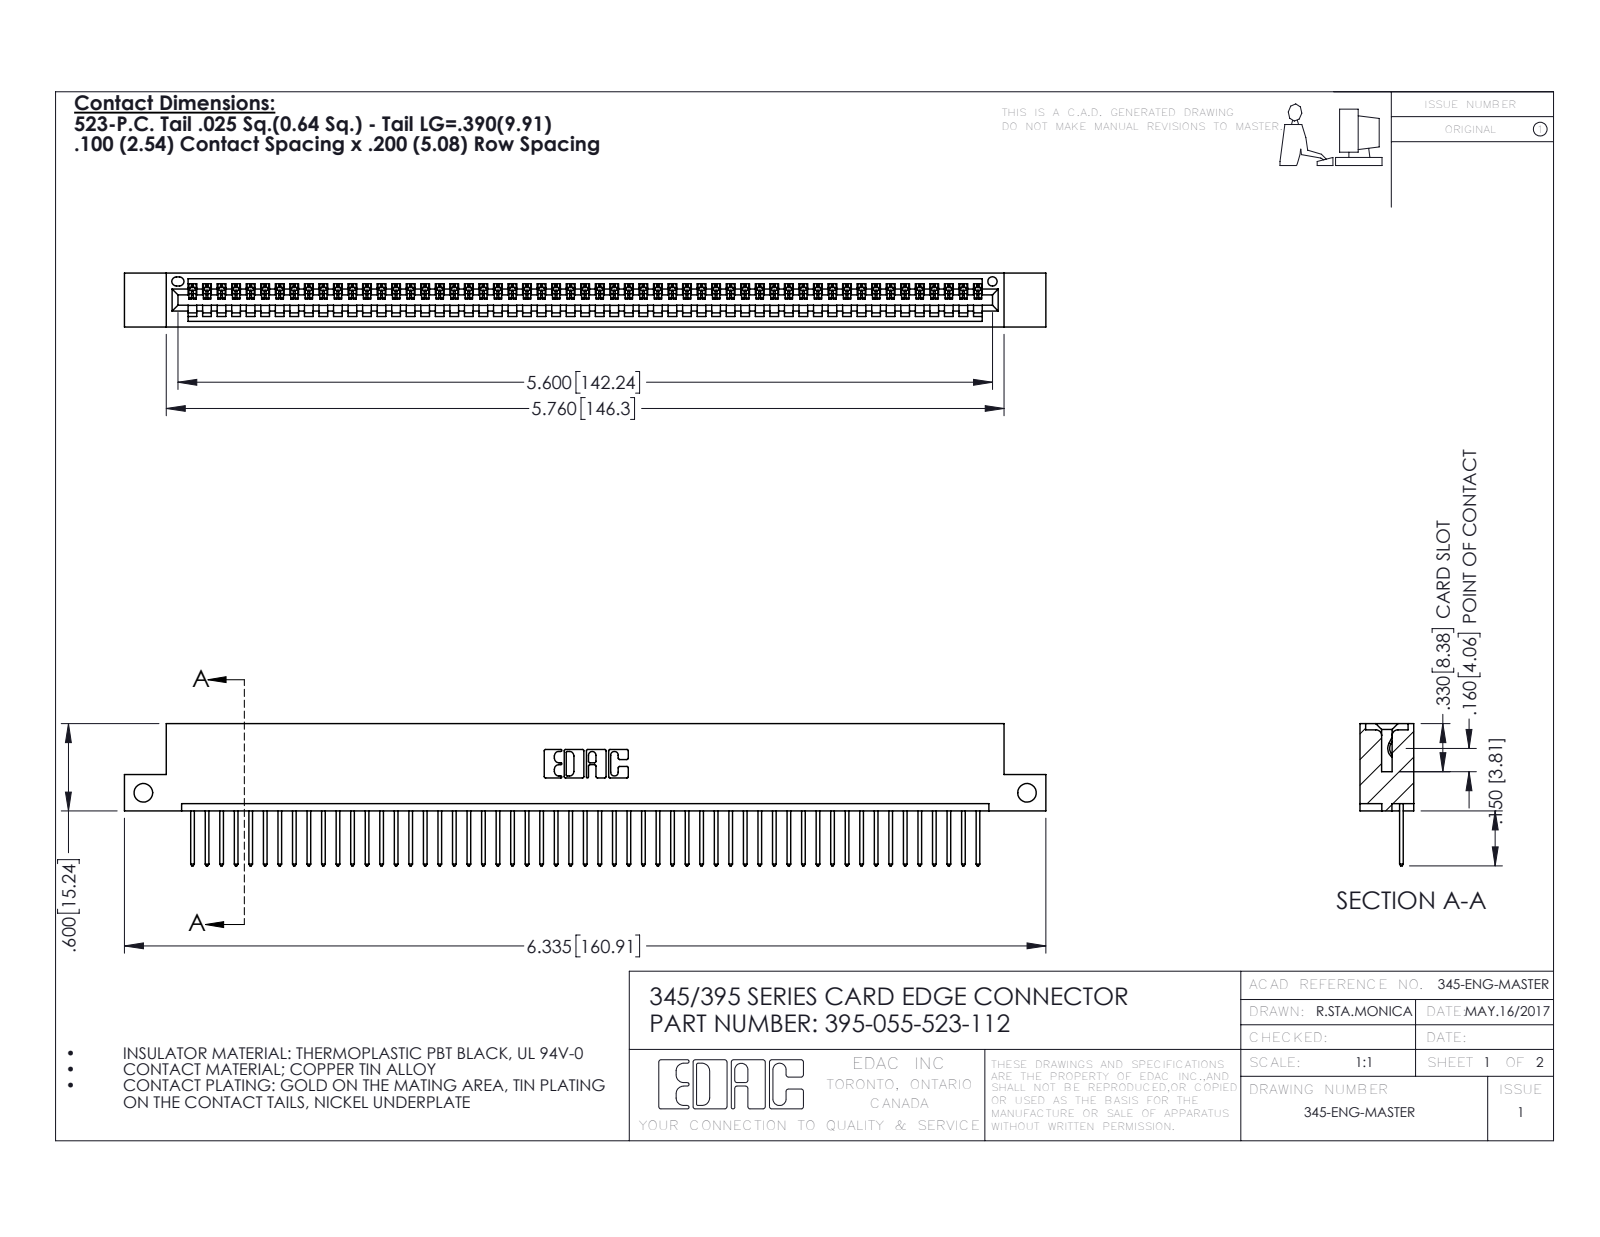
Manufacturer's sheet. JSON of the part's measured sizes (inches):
{"part_name": "395-055-523-112; 345-292-001_345-293-123; 345 Part_Flush Mounting Lugs - Side Mount", "step_written_by": "SolidWorks 2016 (CONFIG_CONTROL_DESIGN)", "units": "inches", "bodies": {"solids": 56, "faces": 3316, "planar": 2280, "cylindrical": 1036, "other": 0}, "overall_size": [6.335, 0.977, 0.37], "volume_in3": 0.933, "surface_area_in2": 31.62, "round_holes": [[0.128, 2], [0.064, 1]], "partial_cylinders_radius": [[0.006, 110], [0.01, 110], [0.01, 22], [0.007, 6], [0.031, 6], [0.026, 3], [0.031, 2], [0.04, 2]], "face_to_face_distances": [0.298, 0.072, 0.37, 0.2, 0.098, 0.272, 0.025, 0.225, 0.149, 0.072], "hole_center_spacings": [6.075]}
